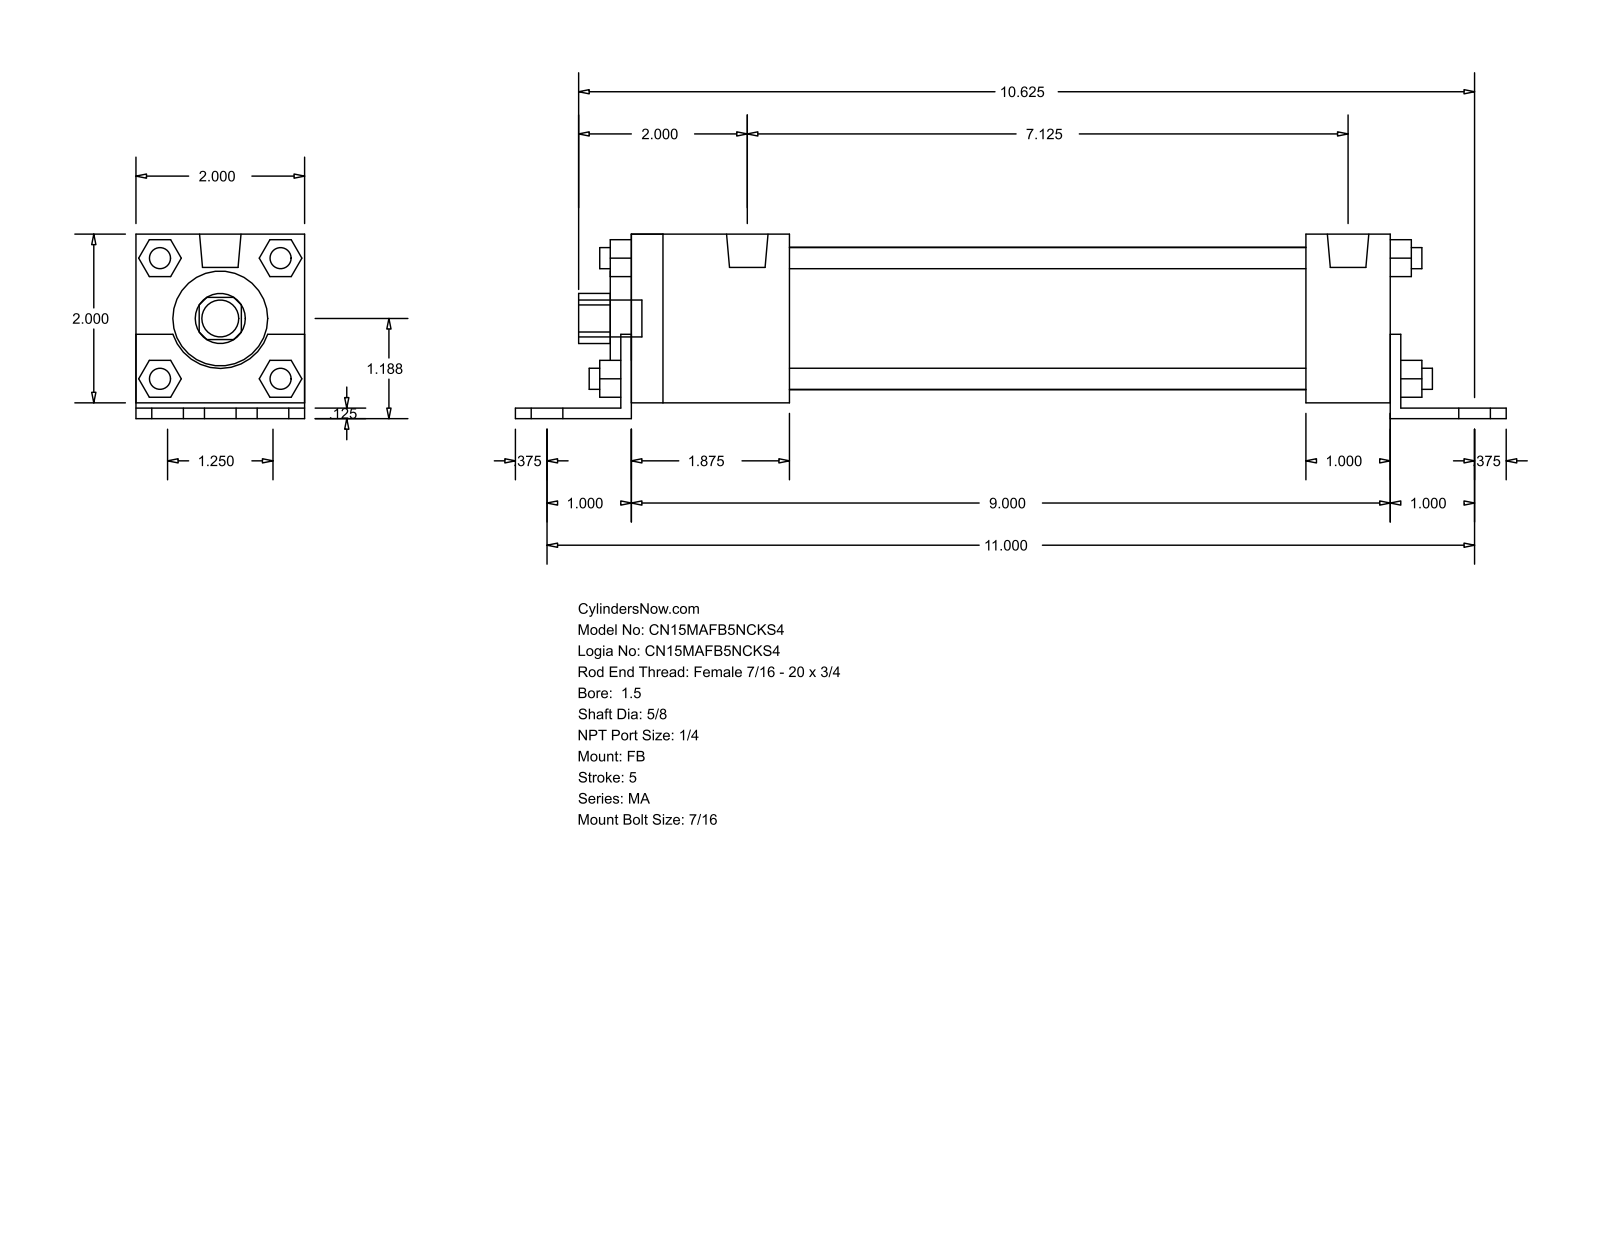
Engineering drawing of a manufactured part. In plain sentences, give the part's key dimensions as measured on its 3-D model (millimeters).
The part is named "MA_FB__0150_0.625". Its 3-D file was written by "GSSL Pune (CONFIG_CONTROL_DESIGN)". It is 0 solids with 140 faces: 105 planar, 35 cylindrical and 0 other. Overall it measures 298.45 by 55.56 by 50.8 millimeters. Round holes: 1 of diameter 15.88, 1 of diameter 28.57, 1 of diameter 42.93. Round bosses or shafts: 7 of diameter 11.11, 4 of diameter 7.94, 4 of diameter 6.35, 2 of diameter 12.49. Partial cylindrical surfaces (rounded edges, fillets, slot ends): 1 of radius 7.54, 1 of radius 15.05. The main face-to-face distances are 50.8, 3.17, 4.76, 55.56, 1.59, 52.39, 3.18, 231.77, 25.4, 238.12.
